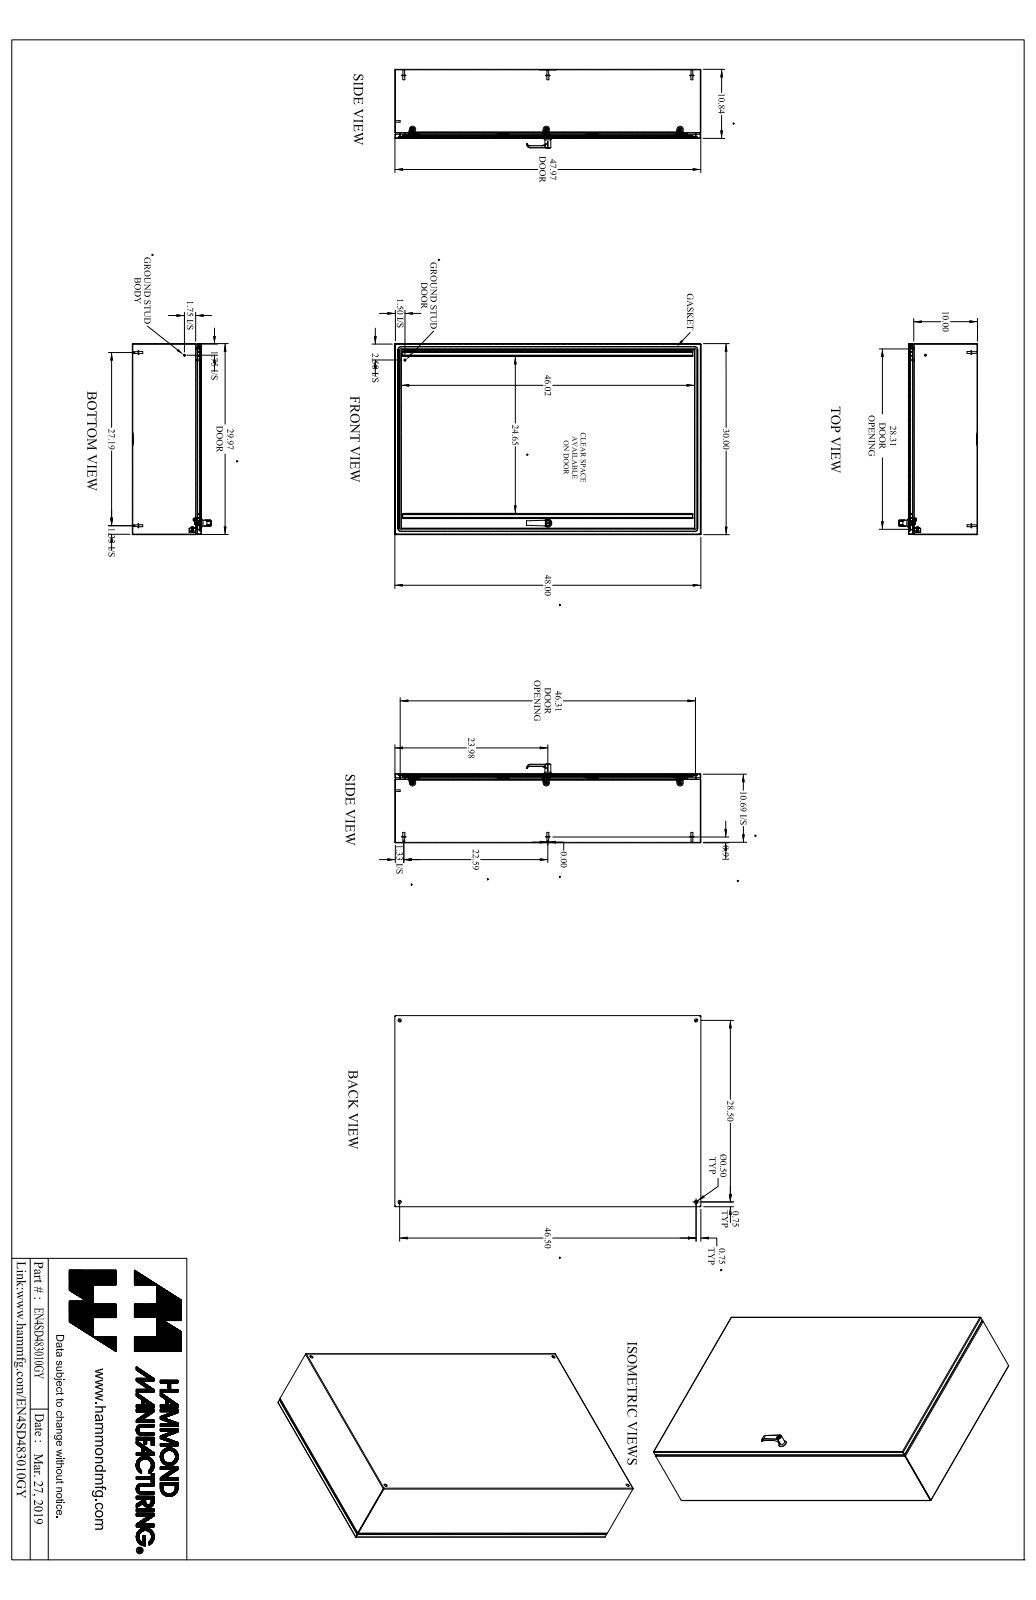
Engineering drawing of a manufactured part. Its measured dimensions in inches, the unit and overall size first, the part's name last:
Units: inches
Overall size (bounding box): 48 × 30 × 12.367
Round holes (diameter × count): ⌀0.176 ×6, ⌀0.5 ×4, ⌀0.196 ×3, ⌀0.25 ×3, ⌀0.265 ×3, ⌀0.413 ×3, ⌀0.256 ×2, ⌀0.313 ×2, ⌀0.394 ×2, ⌀0.172 ×1, ⌀0.24 ×1, ⌀0.242 ×1
Round bosses / shafts (diameter × count): ⌀0.25 ×7, ⌀0.375 ×6, ⌀0.156 ×6, ⌀0.625 ×5, ⌀0.313 ×5, ⌀0.27 ×5, ⌀1 ×3, ⌀0.63 ×2
Partial cylindrical surfaces — rounded edges, fillets, slot ends (radius × count): R0.036 ×20, R0.108 ×20, R0.03 ×15, R0.043 ×12, R0.081 ×12, R0.006 ×8, R0.04 ×8, R0.062 ×8
Main face-to-face distances: 0.072, 10.765, 10.693, 10.837, 29.928, 29.856, 30, 0.072, 47.928, 47.856
Hole centre spacings: 41.969, 0.787, 20.981, 20.988, 21, 27.52, 28.5, 46.5
Volume: 372.3 in³ · Surface area: 10 334 in²
Bodies: 52 solids, 1441 faces (628 planar, 532 cylindrical, 281 other)
Part name (STEP PRODUCT): EN4SD483010GY
STEP written by: SolidWorks 2018 (AUTOMOTIVE_DESIGN)
